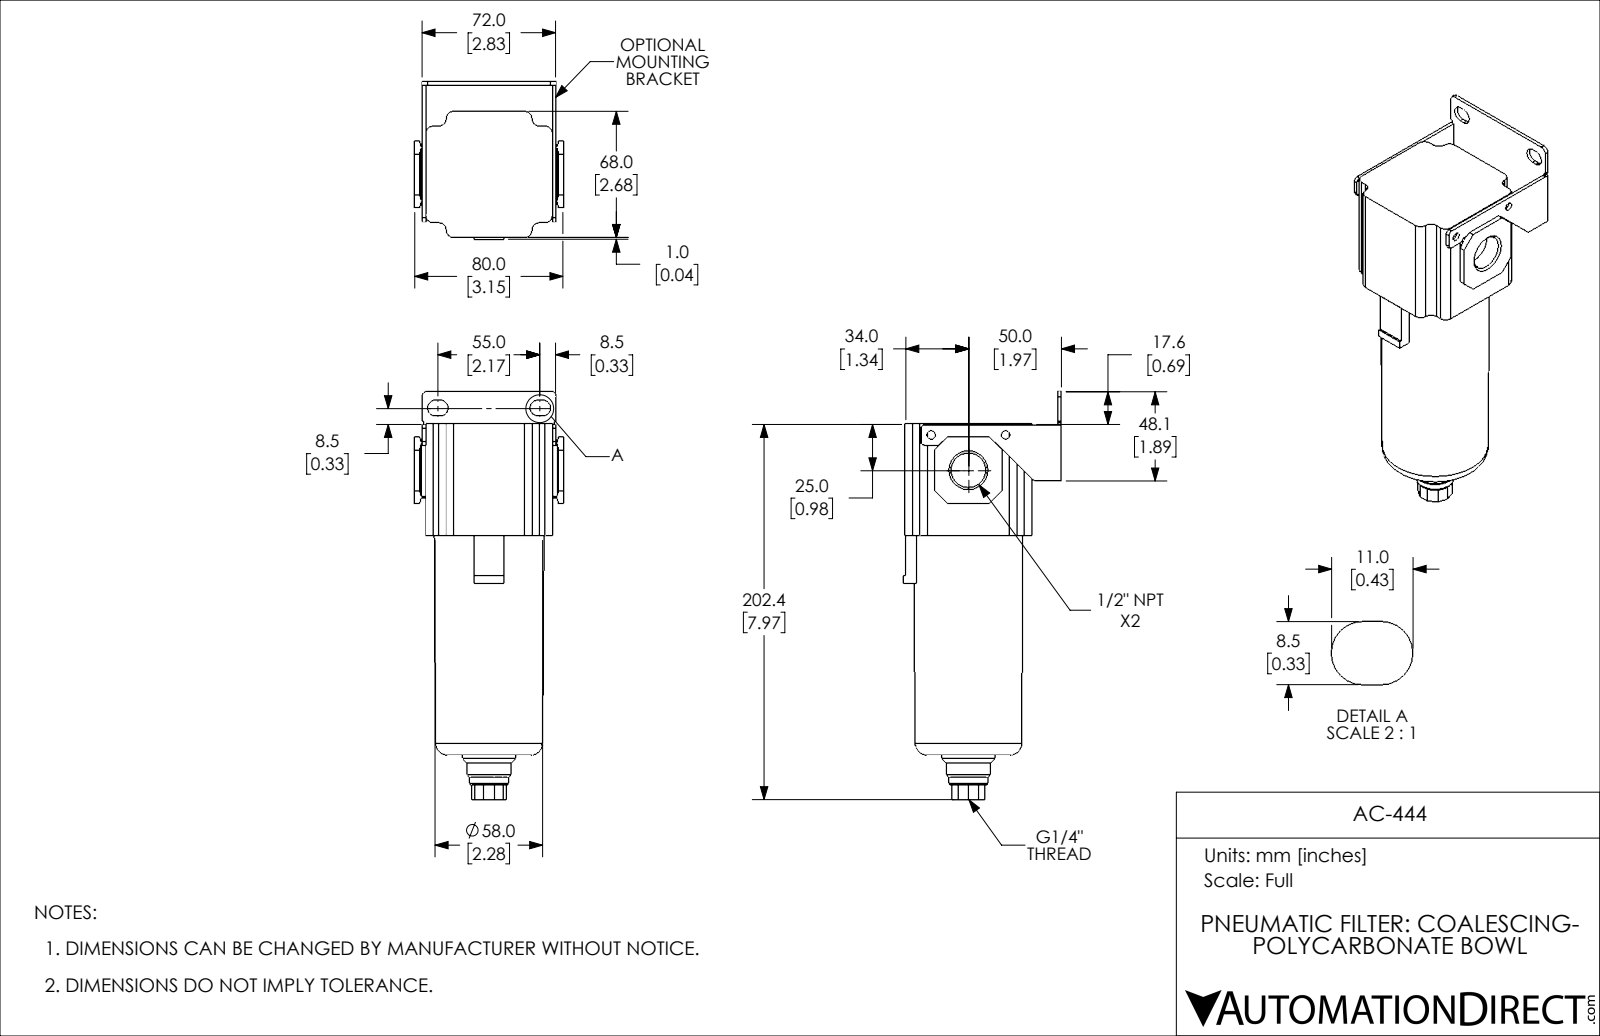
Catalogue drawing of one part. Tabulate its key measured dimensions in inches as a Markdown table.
| quantity | value |
| --- | --- |
| part name | AC-444 |
| STEP written by | SolidWorks 2018 (AUTOMOTIVE_DESIGN) |
| units | inches |
| bodies | 1 solid, 166 faces (102 planar, 48 cylindrical, 16 other) |
| overall size | 8.661 × 3.346 × 3.15 |
| volume | 35.81 in³ |
| surface area | 94.13 in² |
| round holes (diameter × count) | 0.177 × 2, 0.451 × 1, 0.734 × 1 |
| round bosses / shafts (diameter × count) | 1.102 × 1, 0.906 × 1, 0.787 × 1 |
| partial cylindrical surfaces (radius × count) | 0.157 × 12, 0.167 × 4, 0.079 × 3, 0.039 × 2, 0.118 × 2 |
| main face-to-face distances | 0.079, 2.677, 2.756, 0.63, 2.362, 3.307, 0.551, 3.228, 0.157, 0.236 |
| hole center spacings | 1.086, 1.575 |
